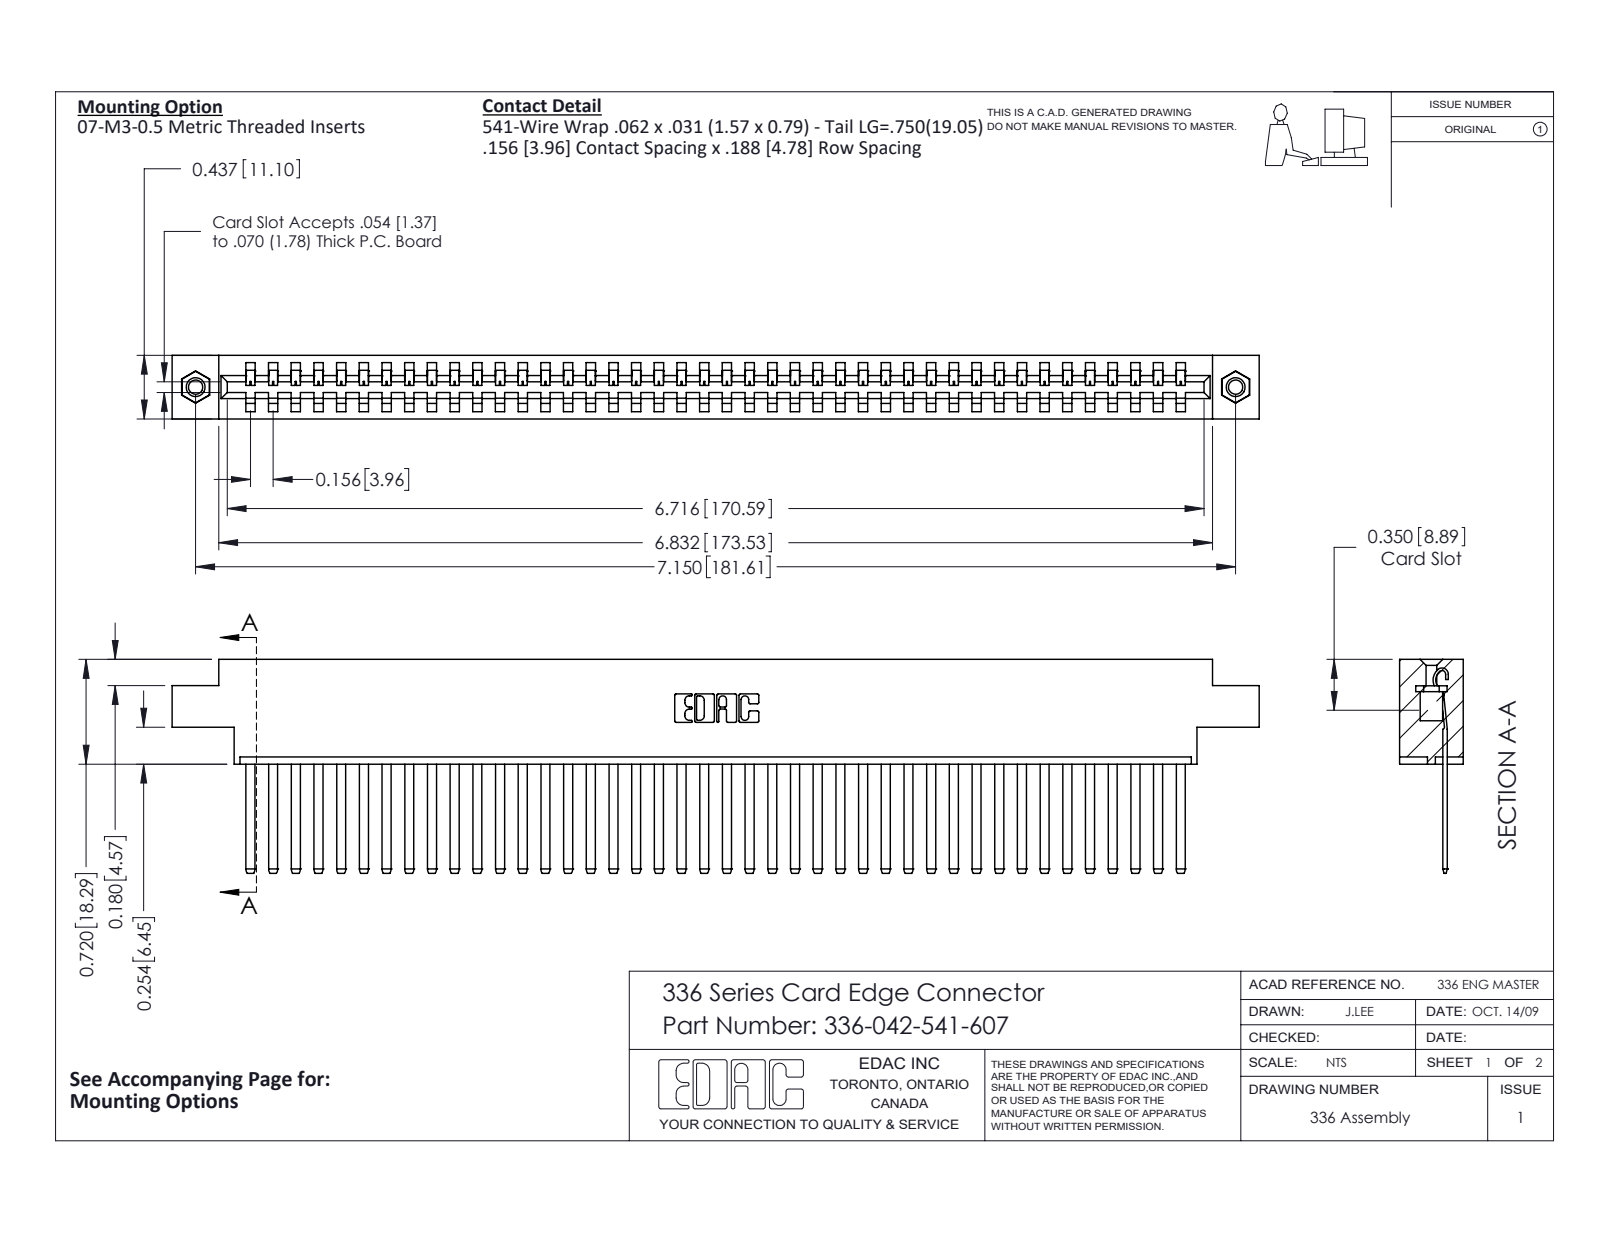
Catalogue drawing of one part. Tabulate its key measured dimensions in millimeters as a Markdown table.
| quantity | value |
| --- | --- |
| part name | 345-250-001_345-250-005-103; 336 Part_Offset - .156 Dia - TI; 336-042-541-607; 336-290-001_336-290-541 |
| STEP written by | SolidWorks 2020 (CONFIG_CONTROL_DESIGN) |
| units | millimeters |
| bodies | 45 solids, 2278 faces (1534 planar, 728 cylindrical, 16 other) |
| overall size | 189.8 × 37.3 × 11.1 |
| volume | 27 640 mm³ |
| surface area | 30 210 mm² |
| round holes (diameter × count) | 2.5 × 2, 3.2 × 2, 4 × 2 |
| round bosses / shafts (diameter × count) | 3.9 × 2 |
| partial cylindrical surfaces (radius × count) | 0.1 × 84, 1.4 × 84, 0.3 × 22, 0.2 × 6, 0.8 × 6, 0.7 × 3, 0.6 × 2, 1 × 2 |
| main face-to-face distances | 11.1, 4.6, 8.3, 3.6, 7.5, 2.8, 0.8, 6.5, 1.3, 3.3 |
| hole center spacings | 181.6 |
